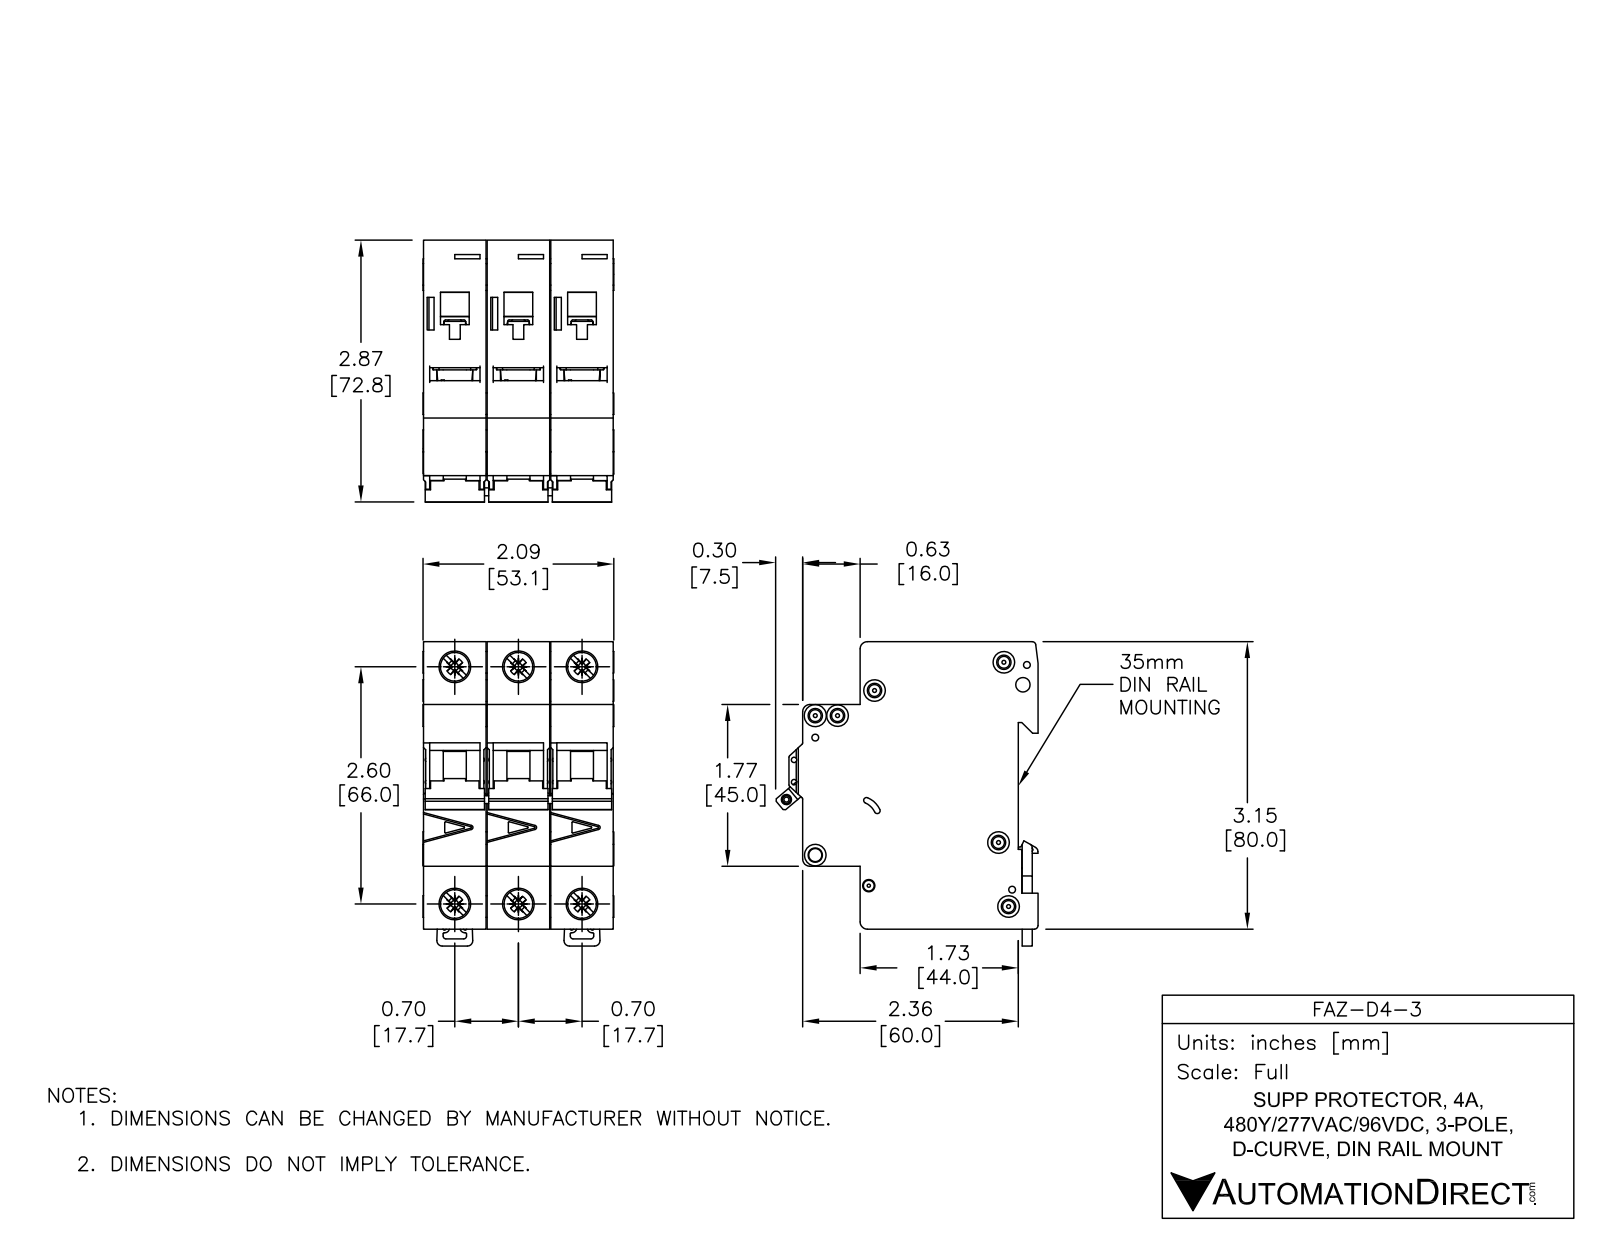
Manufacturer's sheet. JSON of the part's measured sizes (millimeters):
{"part_name": "FAZ-D4-3", "step_written_by": "SolidWorks 2014 (AUTOMOTIVE_DESIGN)", "units": "millimeters", "bodies": {"solids": 11, "faces": 1650, "planar": 697, "cylindrical": 590, "other": 363}, "overall_size": [84.78, 73.04, 53.1], "volume_mm3": 224680, "surface_area_mm2": 58052, "round_holes": [[3.6, 6], [8.2, 4], [1.9, 3], [1.09, 2], [1.5, 2], [4, 2], [7.15, 2], [2.15, 1], [2.2, 1], [2.55, 1], [3.3, 1], [3.4, 1]], "round_bosses_or_shafts": [[6, 4], [2.5, 3], [8.2, 2]], "partial_cylinders_radius": [[0.25, 68], [0.5, 25], [1, 12], [2, 12], [0.2, 11], [1.8, 3], [0.8, 2], [3, 2]], "face_to_face_distances": [17.7, 17.5, 35.4, 35.2, 52.9, 17.9, 79.48, 5.5, 49.5, 44], "hole_center_spacings": [17.7, 68.33, 66, 6.2, 13.64, 35.4, 74.89, 4.81]}
